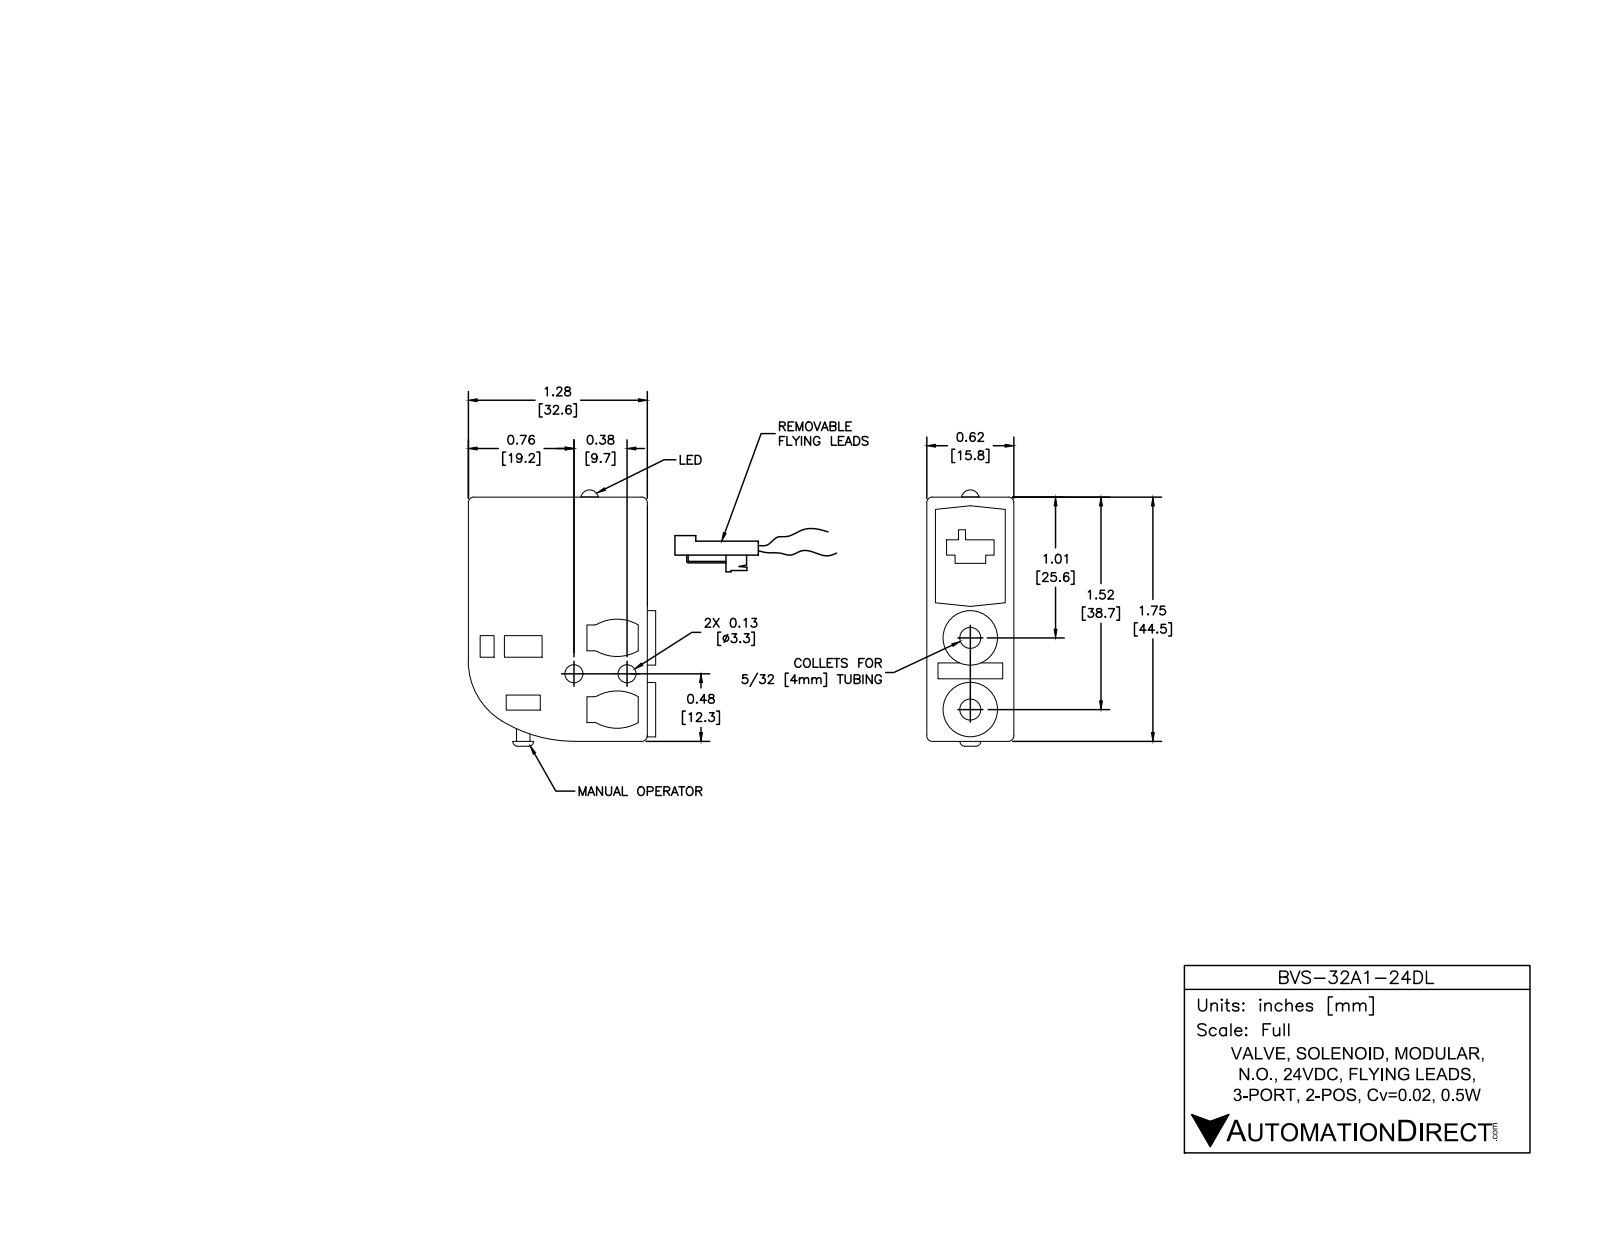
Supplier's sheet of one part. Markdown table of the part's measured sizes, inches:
| quantity | value |
| --- | --- |
| part name | BVS-32A1-24DL |
| STEP written by | SolidWorks 2016 (AUTOMOTIVE_DESIGN) |
| units | inches |
| bodies | 1 solid, 149 faces (83 planar, 54 cylindrical, 12 other) |
| overall size | 1.84 × 1.788 × 0.62 |
| volume | 1.259 in³ |
| surface area | 10.37 in² |
| round holes (diameter × count) | 0.13 × 2, 0.15 × 2, 0.25 × 2, 0.05 × 1 |
| round bosses / shafts (diameter × count) | 0.06 × 6, 0.39 × 2, 0.1 × 1 |
| partial cylindrical surfaces (radius × count) | 0.05 × 4, 0.3 × 4, 0.04 × 3, 0.5 × 1, 1 × 1 |
| main face-to-face distances | 0.62, 0.1, 1.29, 0.52, 1.291, 1.75, 1, 0.15, 0.06, 1.35 |
| hole center spacings | 0.06, 0.38, 0.45, 0.51 |
